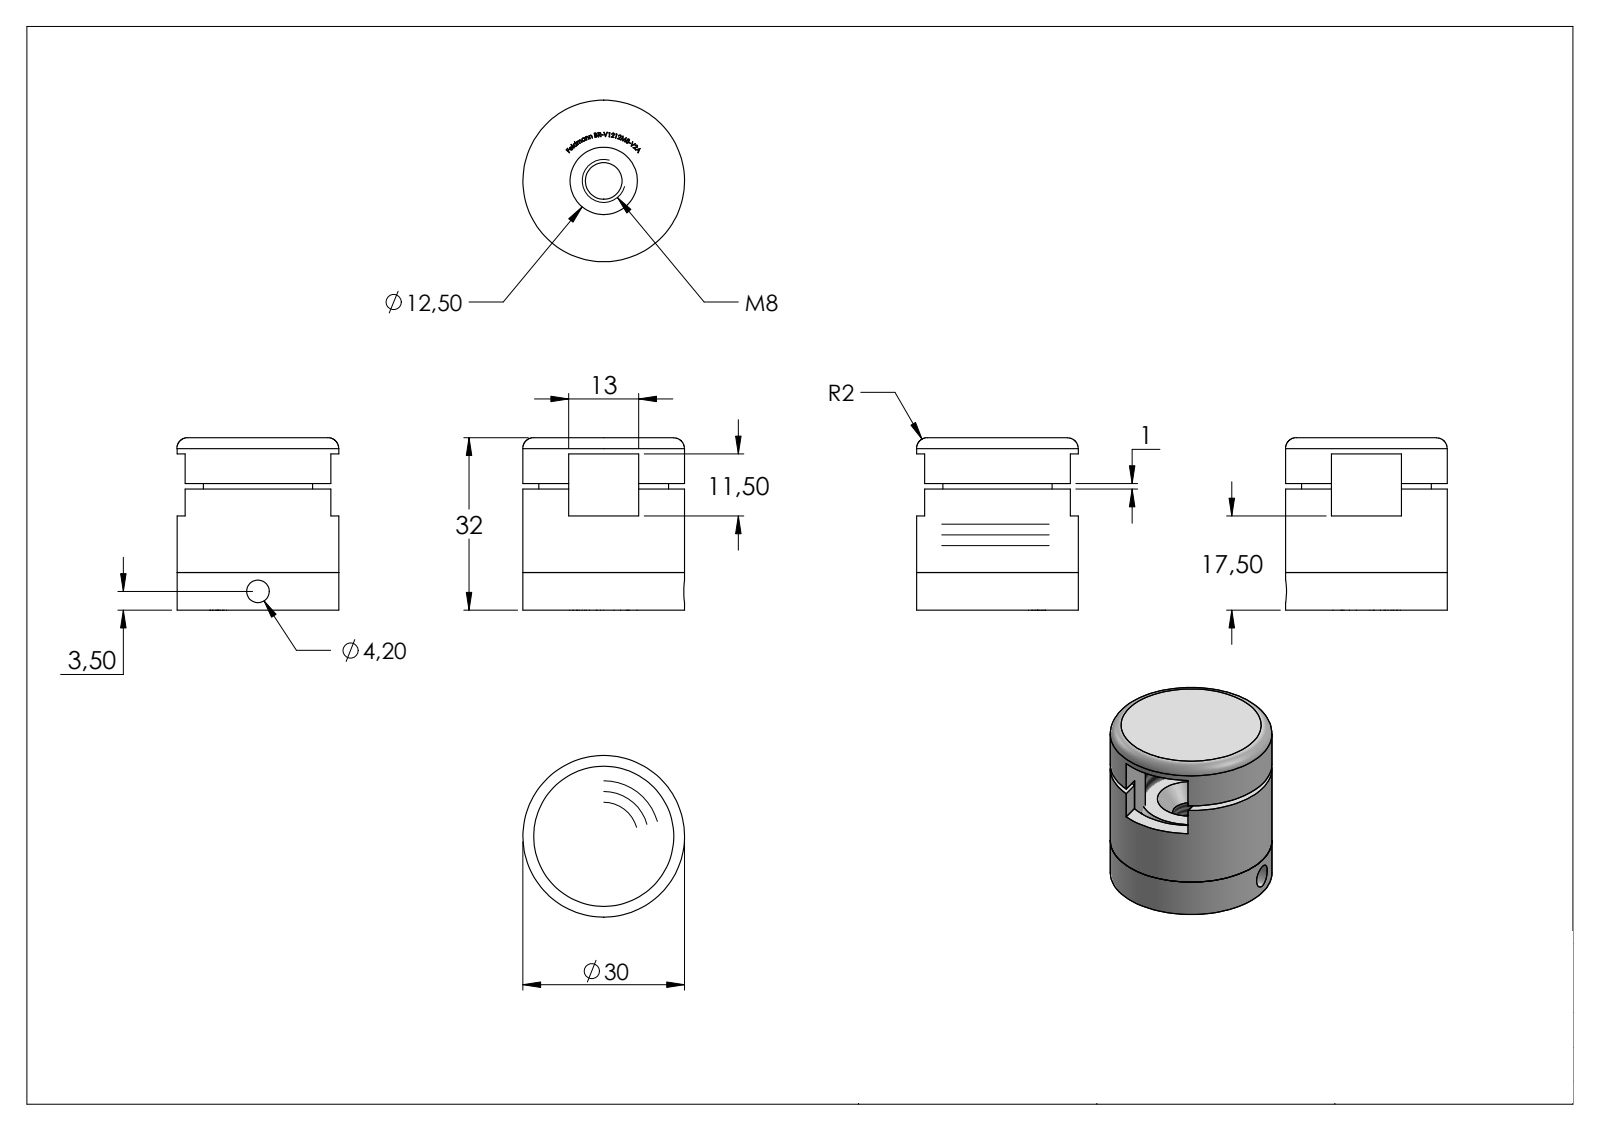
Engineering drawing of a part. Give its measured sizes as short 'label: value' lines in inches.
name: BR-R1XM8-XXX Teil1; BR-R1XM8-XXX Teil2_BR-V1212M8-V2A Teil2; BR-V1212M8-V2A; BR-R1XM8-XXX Teil3_BR-V1212M8-V2A Teil3 (+3 more)
written by: SolidWorks 2015 (CONFIG_CONTROL_DESIGN)
unit: in
bodies: 3 solids, 326 faces (192 planar, 12 cylindrical, 122 other)
size: 2.533 × 1.181 × 1.181
volume: 0.97 in³; area: 14.91 in²
holes: 1× ⌀0.165, 1× ⌀0.268, 1× ⌀0.492, 1× ⌀0.953
bosses: 1× ⌀1.181, 1× ⌀0.787
rounds: 1× R0.344, 1× R0.474
face distances: 0.984, 0.276, 1.26, 0.512, 0.118, 1.142, 0.866, 0.63, 0.256, 0.335
